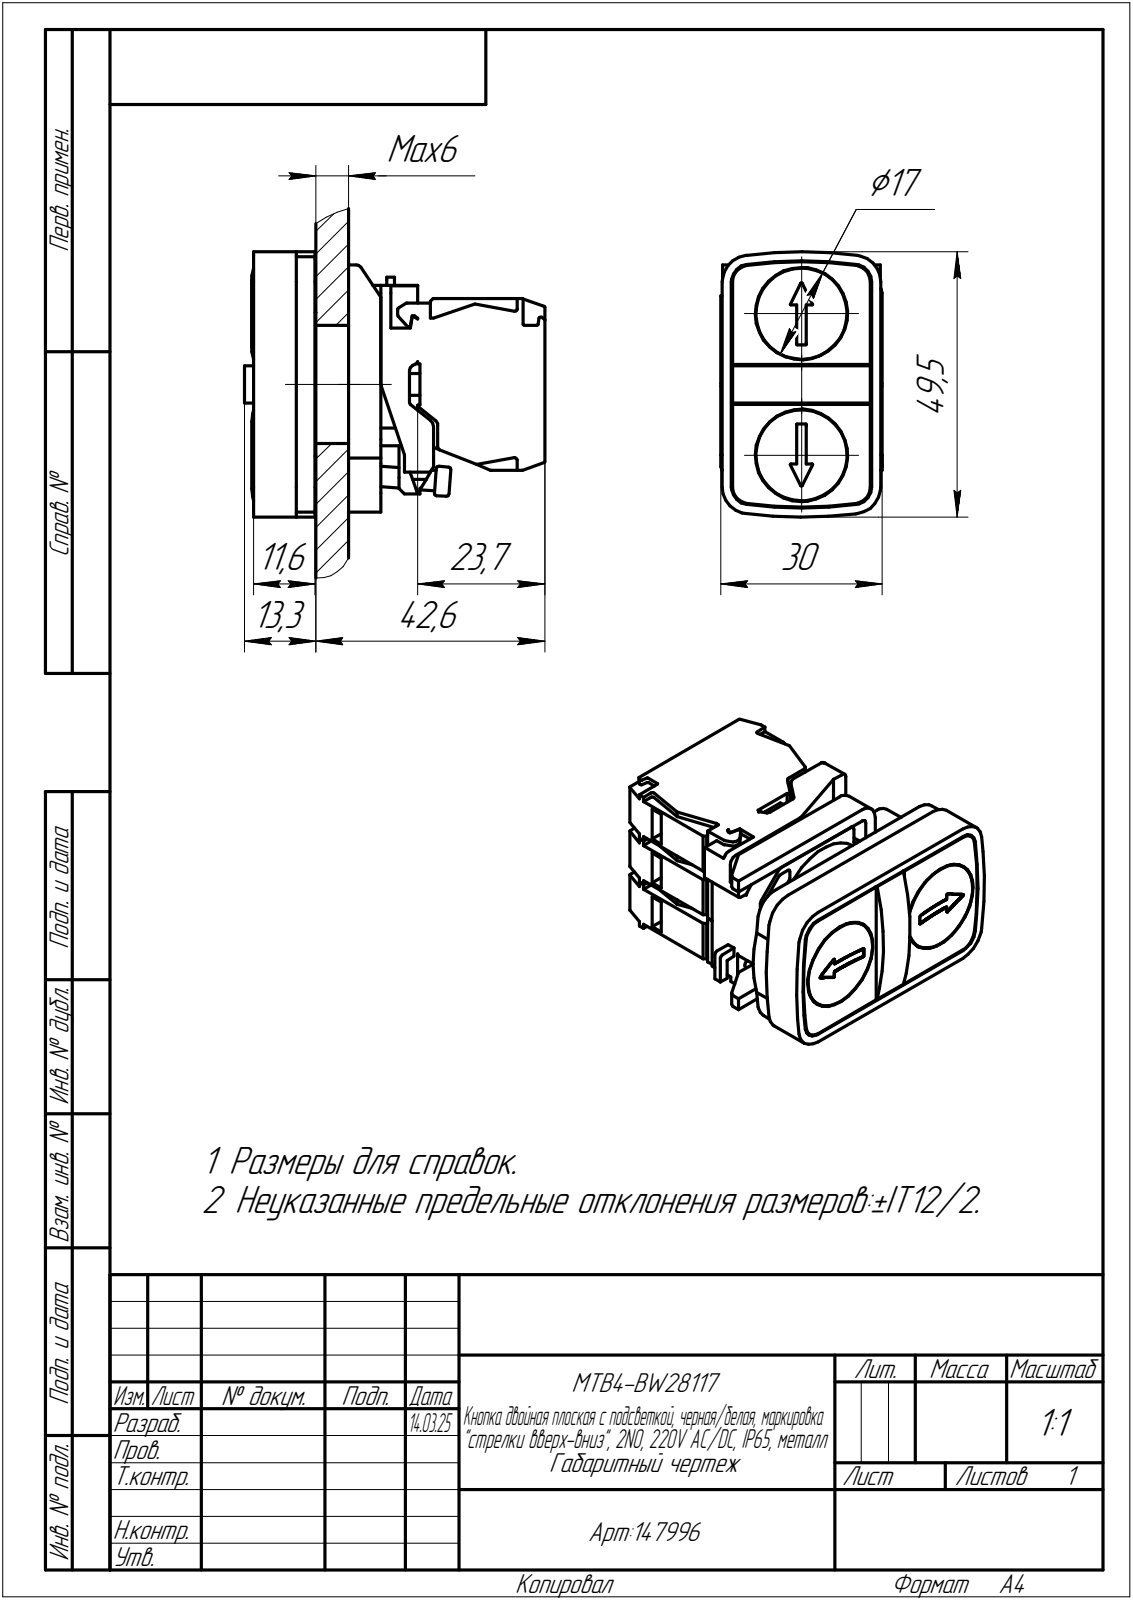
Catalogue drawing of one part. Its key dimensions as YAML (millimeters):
part_name: "MTB4-BW28117"
step_written_by: "C3D Toolkit (CONFIG_CONTROL_DESIGN)"
units: millimeters
bodies: {solids: 2, faces: 646, planar: 426, cylindrical: 190, other: 30}
overall_size: [55.9, 49.5, 30]
volume: 48404
surface_area: 20801
round_holes:
  - {diameter: 1.5, count: 2}
  - {diameter: 6, count: 2}
  - {diameter: 17.2, count: 2}
  - {diameter: 20.5, count: 1}
round_bosses_or_shafts:
  - {diameter: 17, count: 2}
  - {diameter: 26.8, count: 1}
  - {diameter: 22, count: 1}
  - {diameter: 5.5, count: 1}
  - {diameter: 3.8, count: 1}
partial_cylinders:
  - {radius: 0.5, count: 23}
  - {radius: 0.1, count: 10}
  - {radius: 0.2, count: 10}
  - {radius: 0.8, count: 7}
  - {radius: 1, count: 5}
  - {radius: 1.02, count: 4}
  - {radius: 3.1, count: 4}
  - {radius: 3.3, count: 4}
face_to_face_distances: [10, 9.9, 20, 19.9, 10.1, 11.4, 2.5, 29.9, 1.82, 9.75]
hole_center_spacings: [4.7, 8.5, 13.2, 21.7, 11.56, 11.88, 12.63, 13.77]
